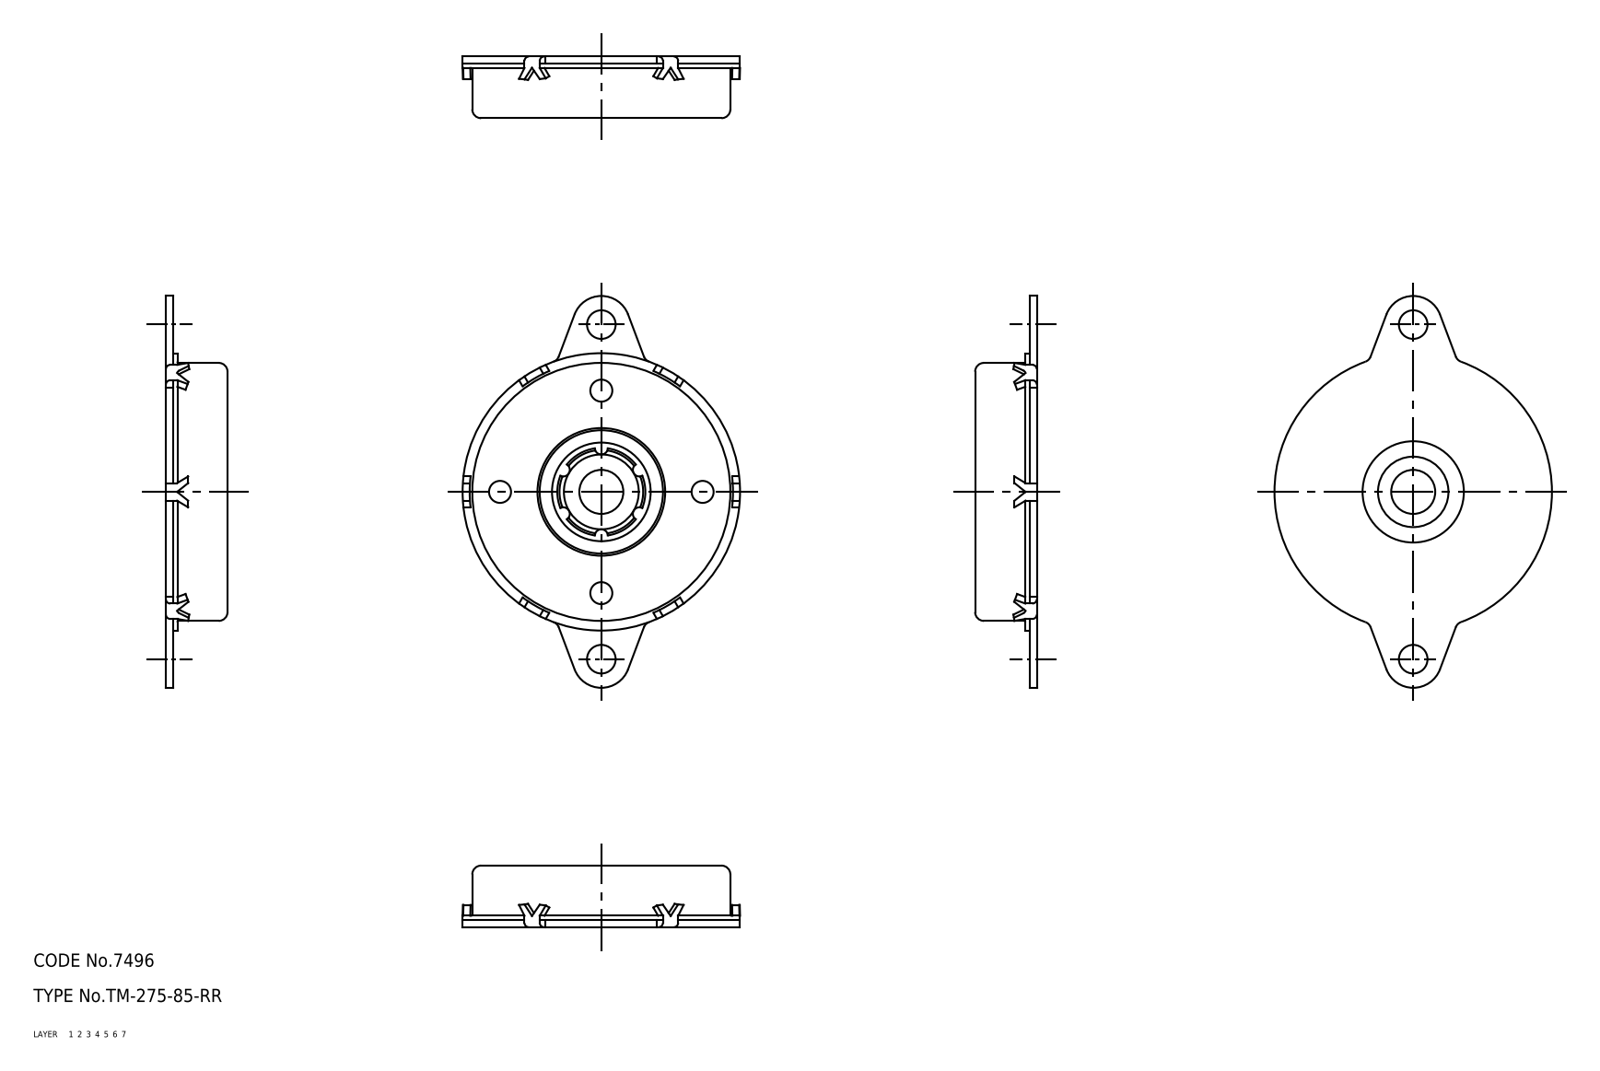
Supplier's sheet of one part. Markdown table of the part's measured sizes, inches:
| quantity | value |
| --- | --- |
| part name | 67120246; 67120259 |
| STEP written by | CADfix (AUTOMOTIVE_DESIGN) |
| units | inches |
| bodies | 2 solids, 218 faces (0 planar, 0 cylindrical, 218 other) |
| overall size | 3.504 × 2.48 × 0.551 |
| volume | 2.201 in³ |
| surface area | 21.08 in² |
